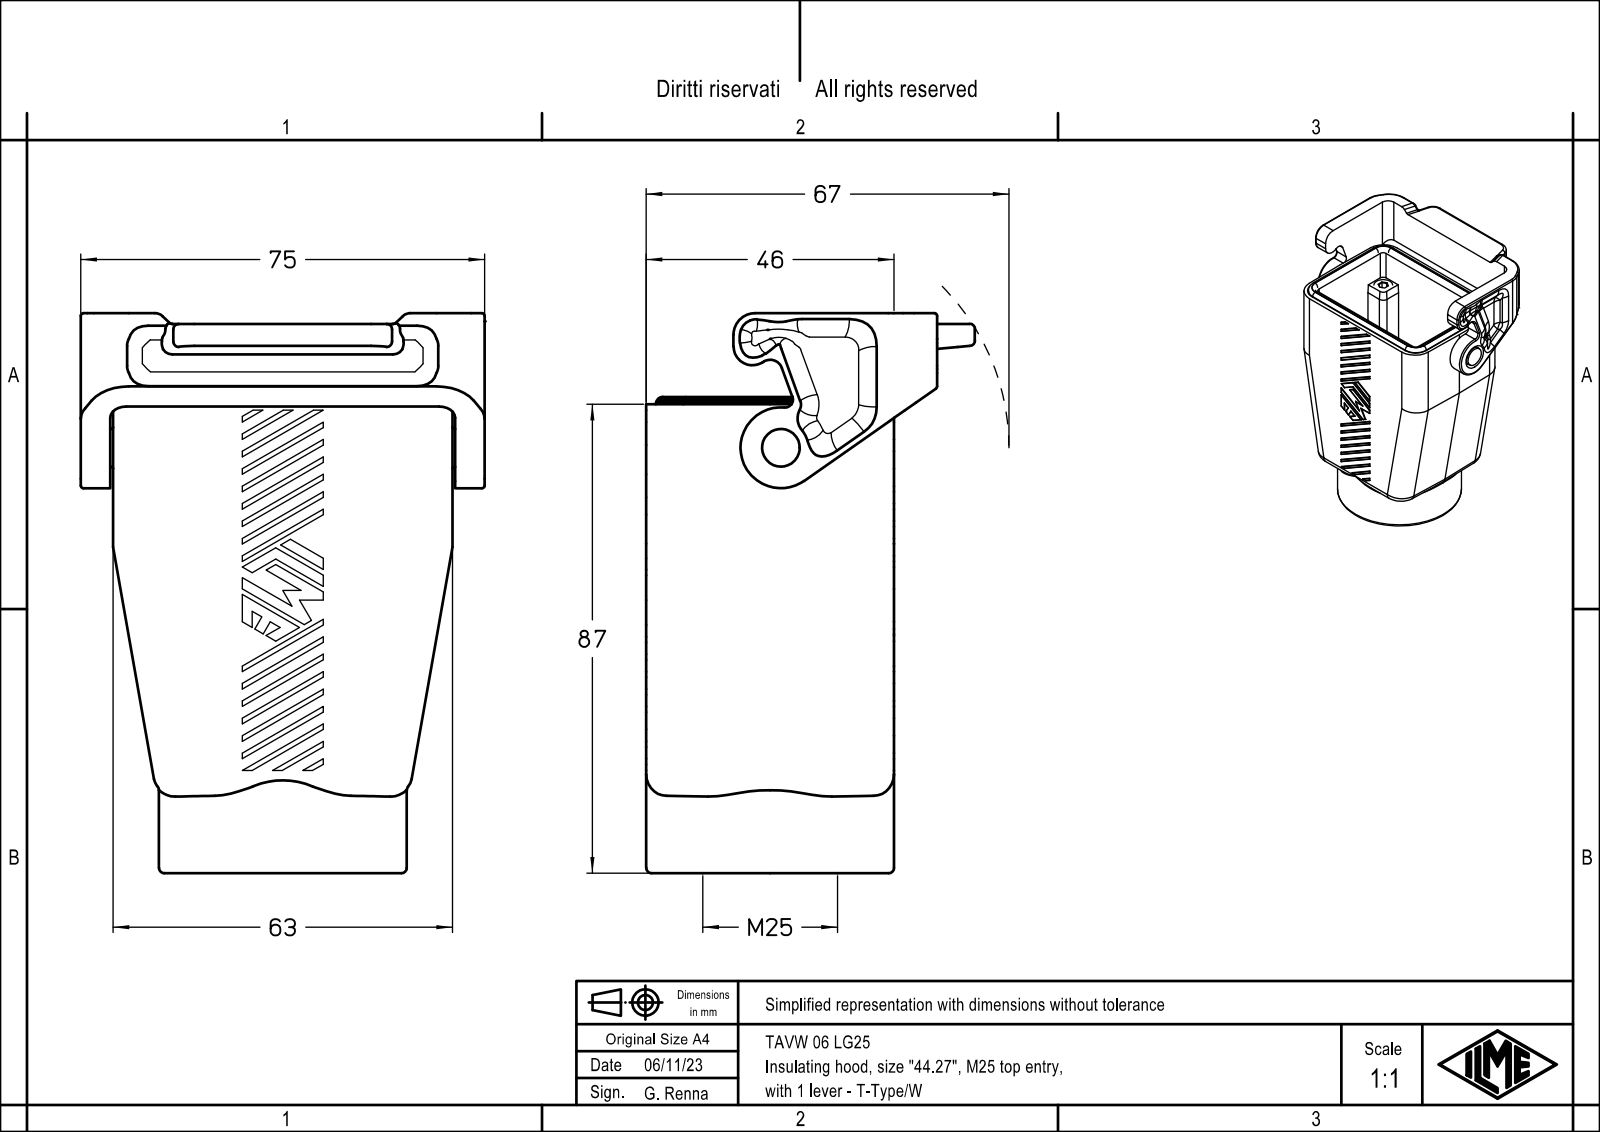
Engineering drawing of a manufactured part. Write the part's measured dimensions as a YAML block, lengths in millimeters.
part_name: "TAVW 06 LG25"
step_written_by: "Creo Elements/Direct Modeling 20.1B 02-Apr-2019 (C) Parametric Technology GmbH (AUTOMOTIVE_DESIGN)"
units: millimeters
bodies: {solids: 1, faces: 546, planar: 188, cylindrical: 306, other: 52}
overall_size: [103.9, 75, 61.15]
volume: 116497
surface_area: 40467
round_holes:
  - {diameter: 21, count: 1}
  - {diameter: 23.6, count: 1}
round_bosses_or_shafts:
  - {diameter: 46, count: 1}
  - {diameter: 7, count: 1}
partial_cylinders:
  - {radius: 0.15, count: 128}
  - {radius: 3, count: 13}
  - {radius: 2, count: 10}
  - {radius: 1, count: 8}
  - {radius: 1.3, count: 8}
  - {radius: 7, count: 8}
  - {radius: 1.5, count: 7}
  - {radius: 6, count: 4}
face_to_face_distances: [5.4, 40.6, 46, 35.2, 5.9, 58.1, 3, 20.5, 49, 43.6]
